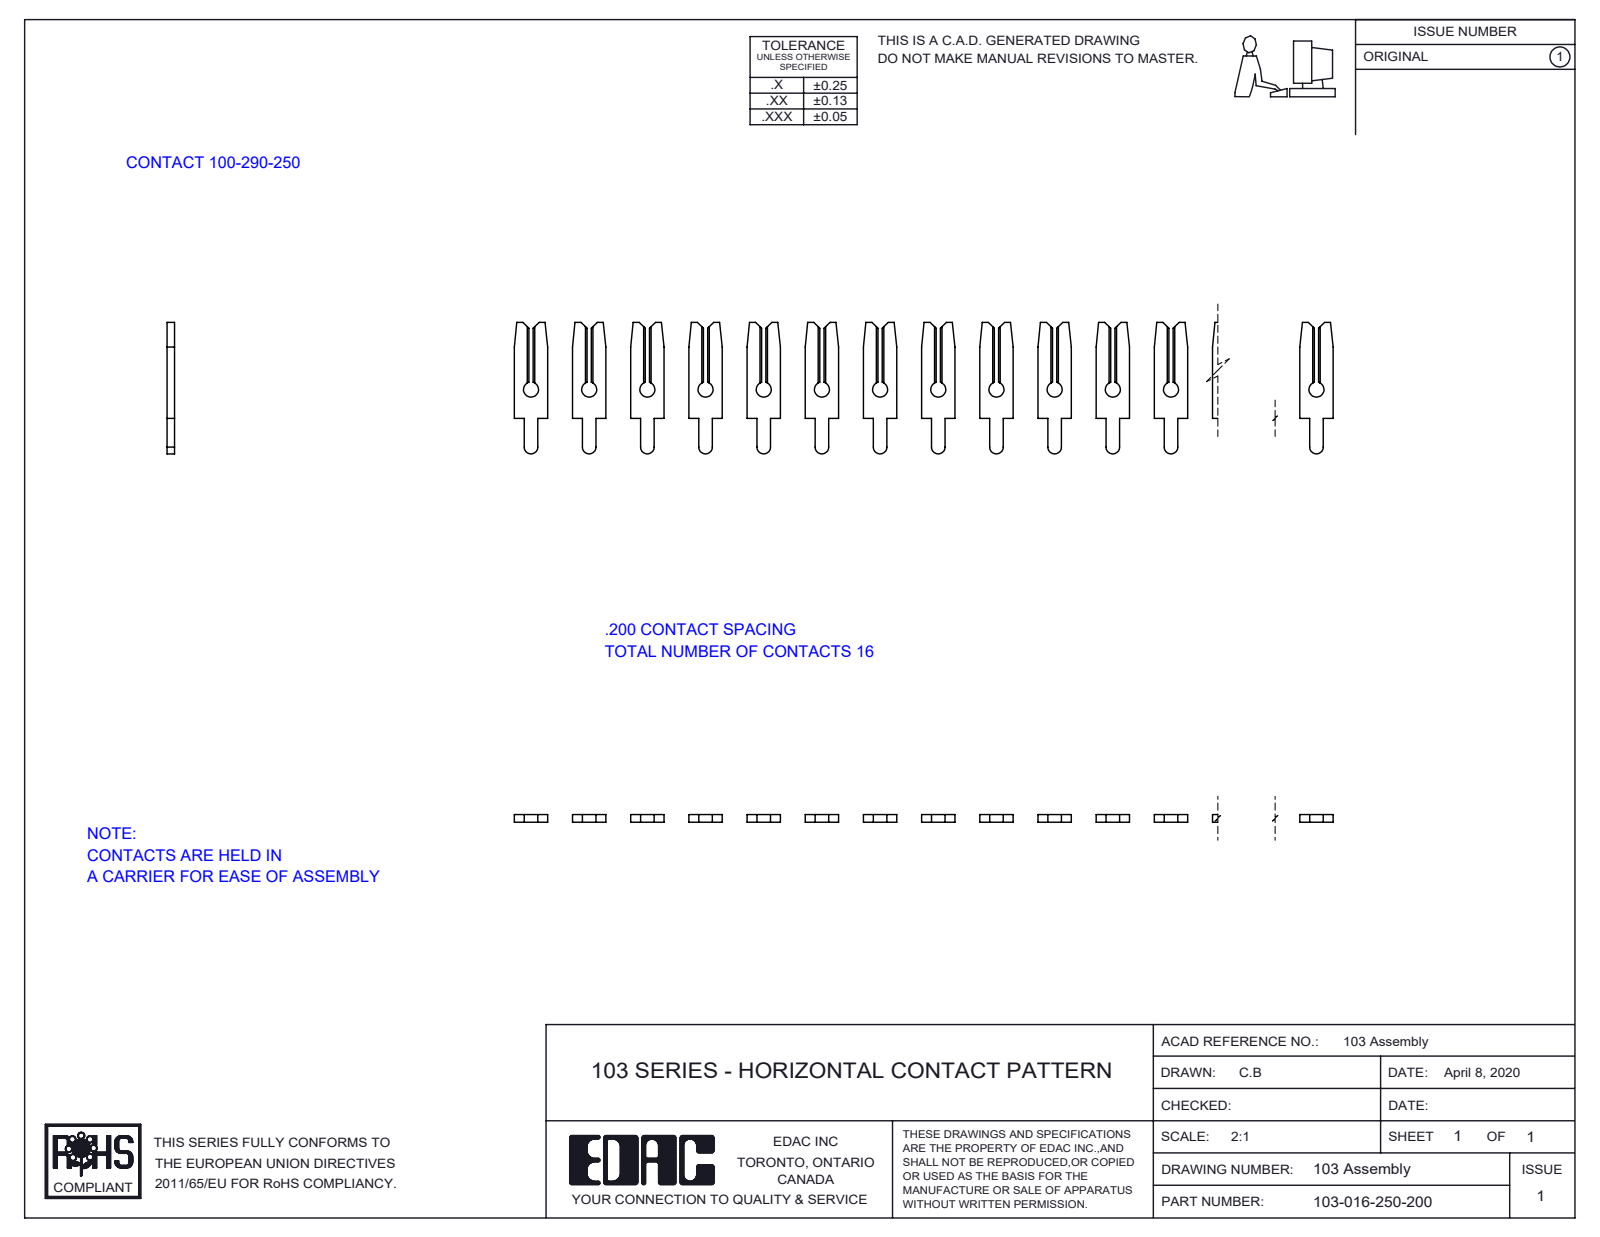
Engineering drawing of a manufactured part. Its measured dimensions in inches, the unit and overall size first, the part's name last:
Units: inches
Overall size (bounding box): 3.115 × 0.452 × 0.026
Round holes (diameter × count): ⌀0.052 ×16
Partial cylindrical surfaces — rounded edges, fillets, slot ends (radius × count): R0.024 ×16
Main face-to-face distances: 0.026, 0.2, 0.4, 0.141, 0.6, 0.8, 0.848, 0.283, 0.707, 0.115
Hole centre spacings: 0.2, 0.4, 0.6, 0.8, 1, 1.2, 1.4, 1.6
Volume: 0.015 in³ · Surface area: 1.819 in²
Bodies: 16 solids, 384 faces (320 planar, 64 cylindrical, 0 other)
Part name (STEP PRODUCT): 100-290-001_100-290-250; 103-016-250-200
STEP written by: SolidWorks 2016 (CONFIG_CONTROL_DESIGN)
